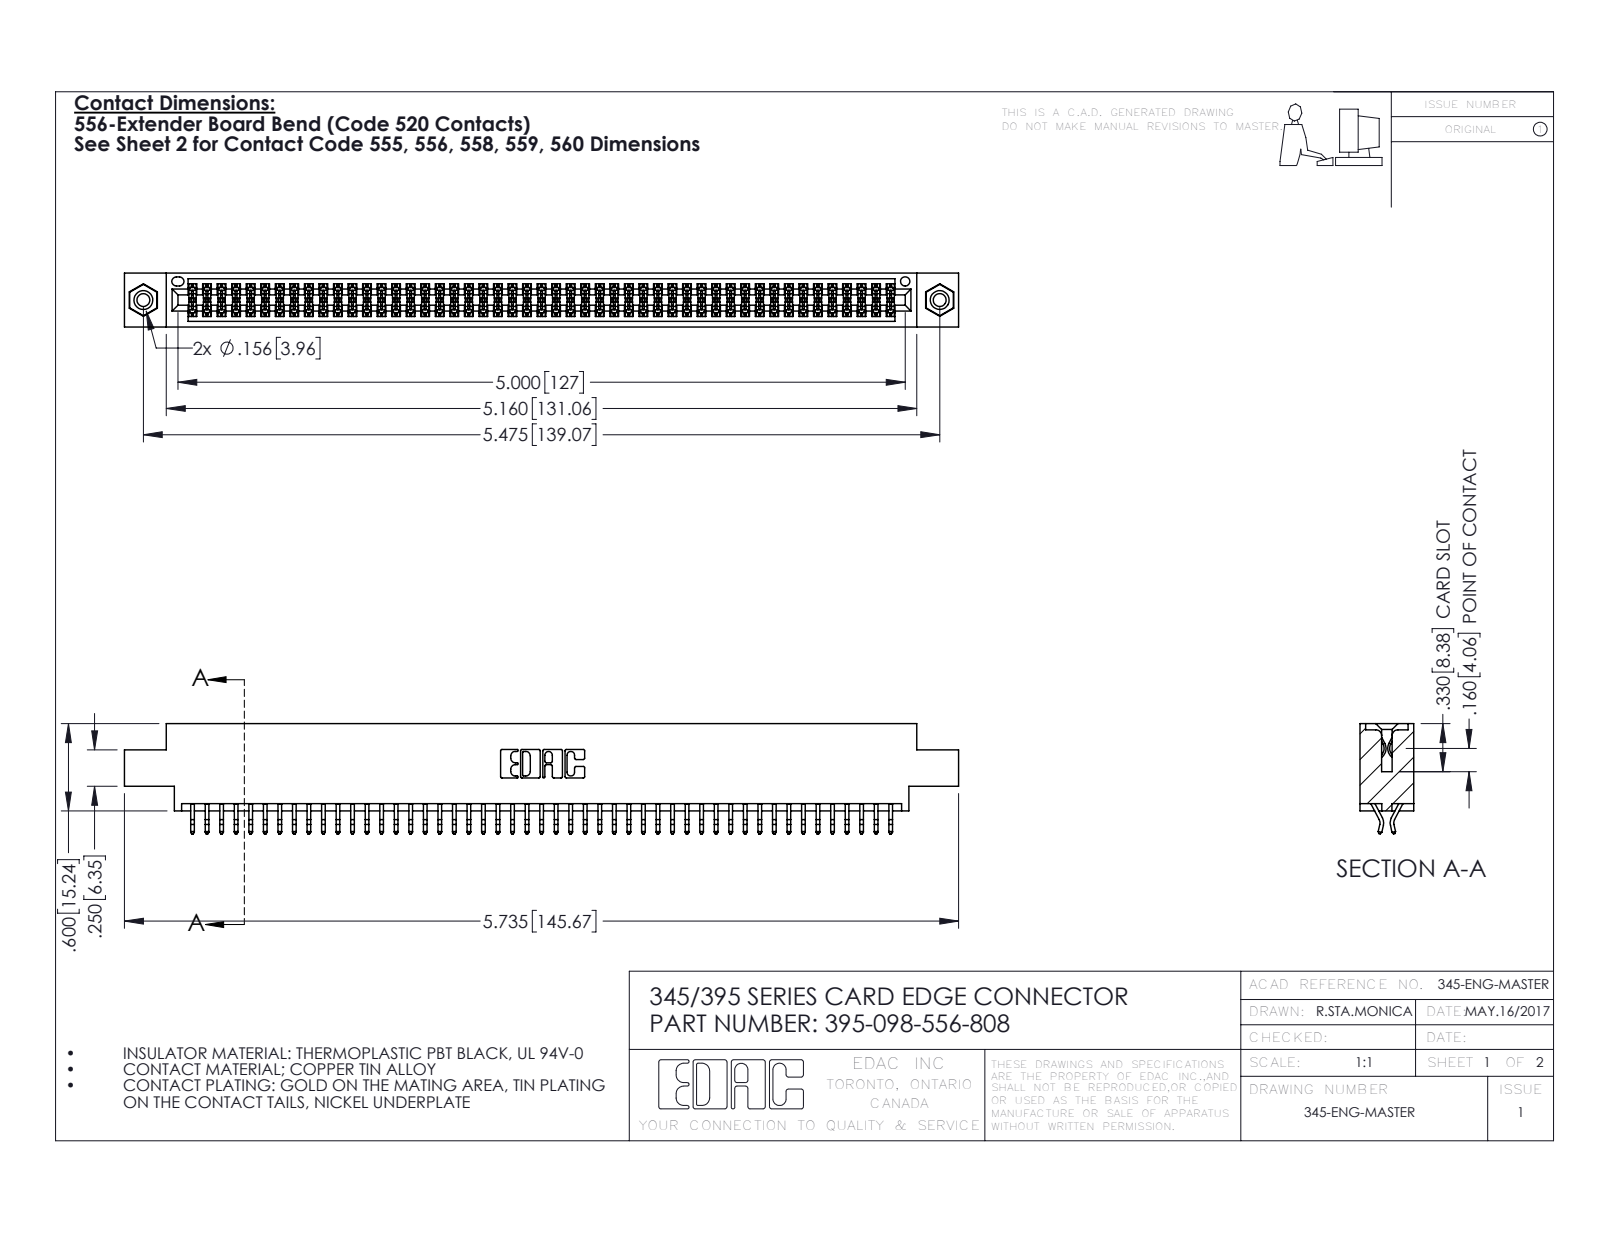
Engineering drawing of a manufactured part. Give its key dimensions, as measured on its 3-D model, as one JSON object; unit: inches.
{"part_name": "345-292-001_556 Tail; 345-250-001_345-250-003-102; 345 Part_0.170 Offset - 0.156 Dia-TI; 395-098-556-808", "step_written_by": "SolidWorks 2016 (CONFIG_CONTROL_DESIGN)", "units": "inches", "bodies": {"solids": 101, "faces": 5678, "planar": 3742, "cylindrical": 1920, "other": 16}, "overall_size": [5.735, 0.757, 0.37], "volume_in3": 0.86, "surface_area_in2": 32.61, "round_holes": [[0.089, 2], [0.125, 2], [0.156, 2], [0.064, 1]], "round_bosses_or_shafts": [[0.155, 2]], "partial_cylinders_radius": [[0.006, 147], [0.01, 22], [0.007, 6], [0.031, 6], [0.026, 3], [0.01, 2], [0.014, 2], [0.019, 2]], "face_to_face_distances": [0.072, 0.298, 0.37, 0.2, 0.025, 0.098, 0.272, 0.225, 0.175, 0.149], "hole_center_spacings": [0.27, 5.239, 5.475]}
